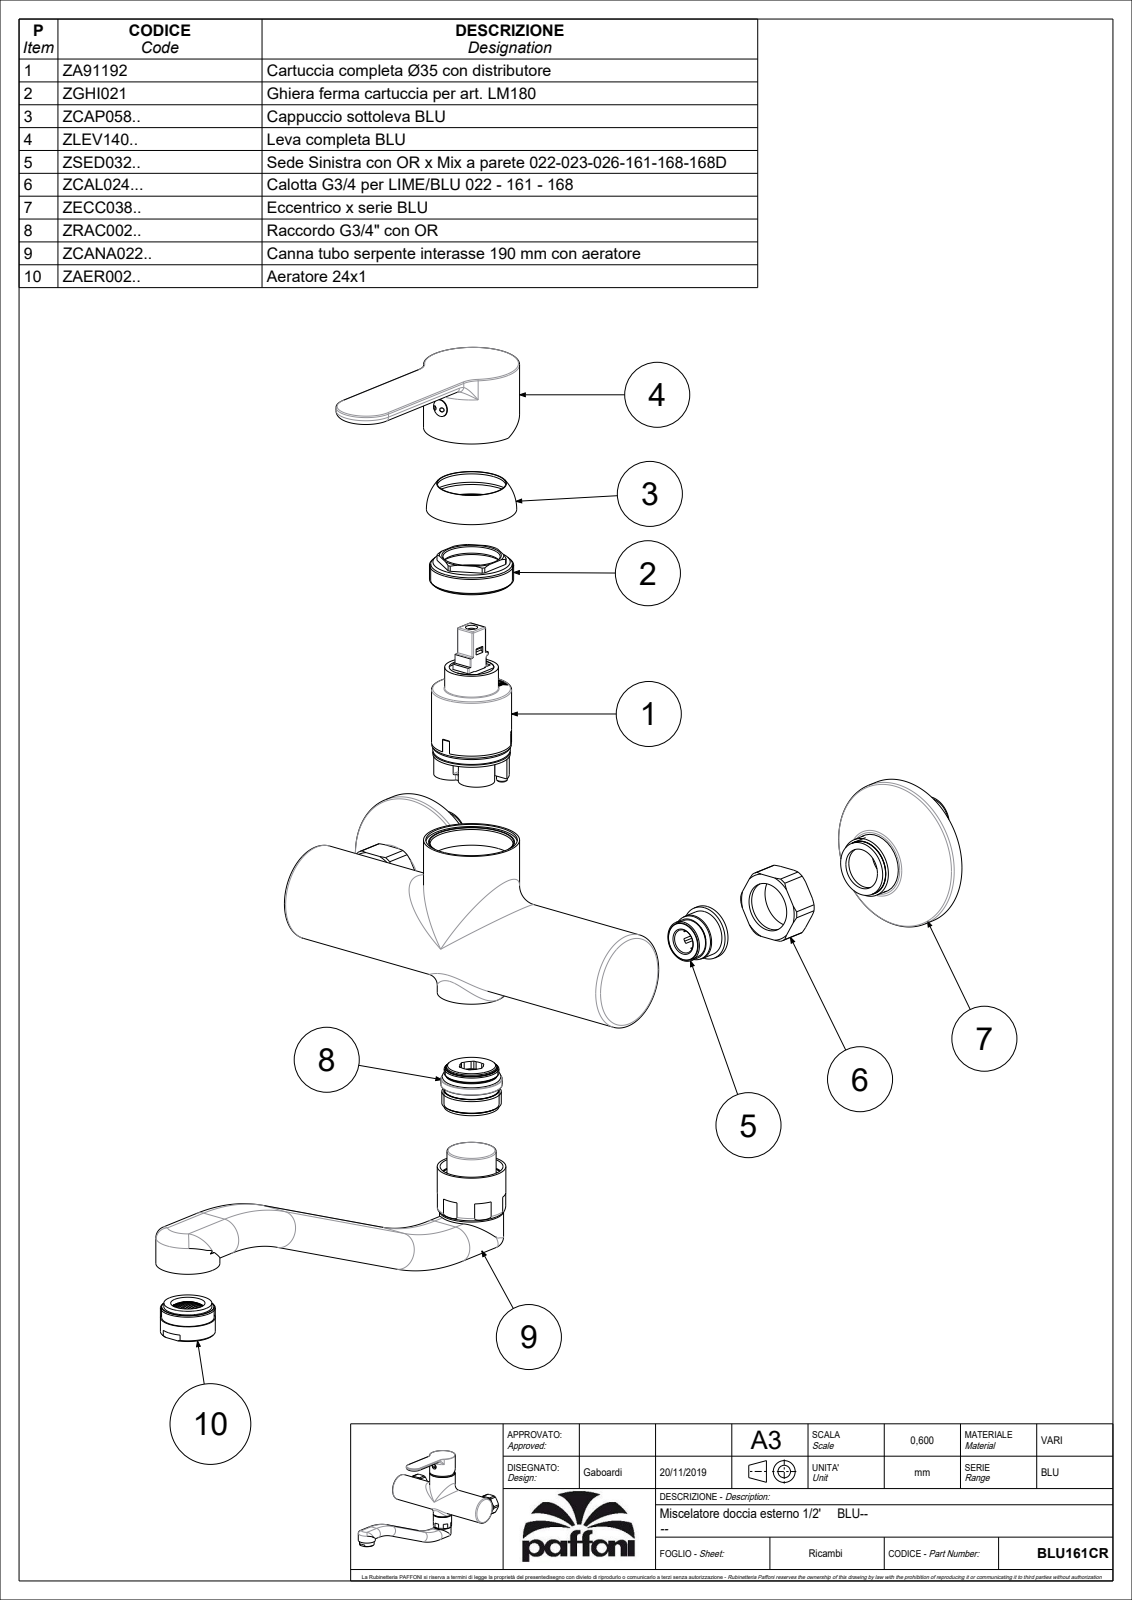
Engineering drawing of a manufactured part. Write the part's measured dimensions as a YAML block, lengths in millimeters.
part_name: "BLU161CR"
step_written_by: "CREO PARAMETRIC BY PTC INC, 2020044 (CONFIG_CONTROL_DESIGN)"
units: millimeters
bodies: {solids: 6, faces: 2710, planar: 1927, cylindrical: 446, other: 337}
overall_size: [263.2, 215.5, 141.8]
volume: 166124
surface_area: 170064
round_holes:
  - {diameter: 12, count: 5}
  - {diameter: 9, count: 3}
  - {diameter: 17, count: 3}
  - {diameter: 3.3, count: 2}
  - {diameter: 7, count: 2}
  - {diameter: 8, count: 2}
  - {diameter: 16, count: 2}
  - {diameter: 16.3, count: 2}
  - {diameter: 18, count: 2}
  - {diameter: 21.5, count: 2}
  - {diameter: 24.1, count: 2}
  - {diameter: 38, count: 2}
round_bosses_or_shafts:
  - {diameter: 24, count: 3}
  - {diameter: 65.5, count: 2}
  - {diameter: 42, count: 2}
  - {diameter: 28.32, count: 2}
  - {diameter: 28, count: 2}
  - {diameter: 25, count: 2}
  - {diameter: 23.8, count: 2}
  - {diameter: 20.8, count: 2}
partial_cylinders:
  - {radius: 0.5, count: 64}
  - {radius: 0.3, count: 20}
  - {radius: 1, count: 13}
  - {radius: 1.2, count: 9}
  - {radius: 7.2, count: 6}
  - {radius: 8, count: 6}
  - {radius: 5.25, count: 3}
  - {radius: 7.25, count: 3}
face_to_face_distances: [2, 69, 109, 0.8, 178, 15.2, 20, 111, 67, 16]
hole_center_spacings: [0.71, 8.51, 8.6, 13.04, 13.21, 13.51, 97.31, 187.61]
